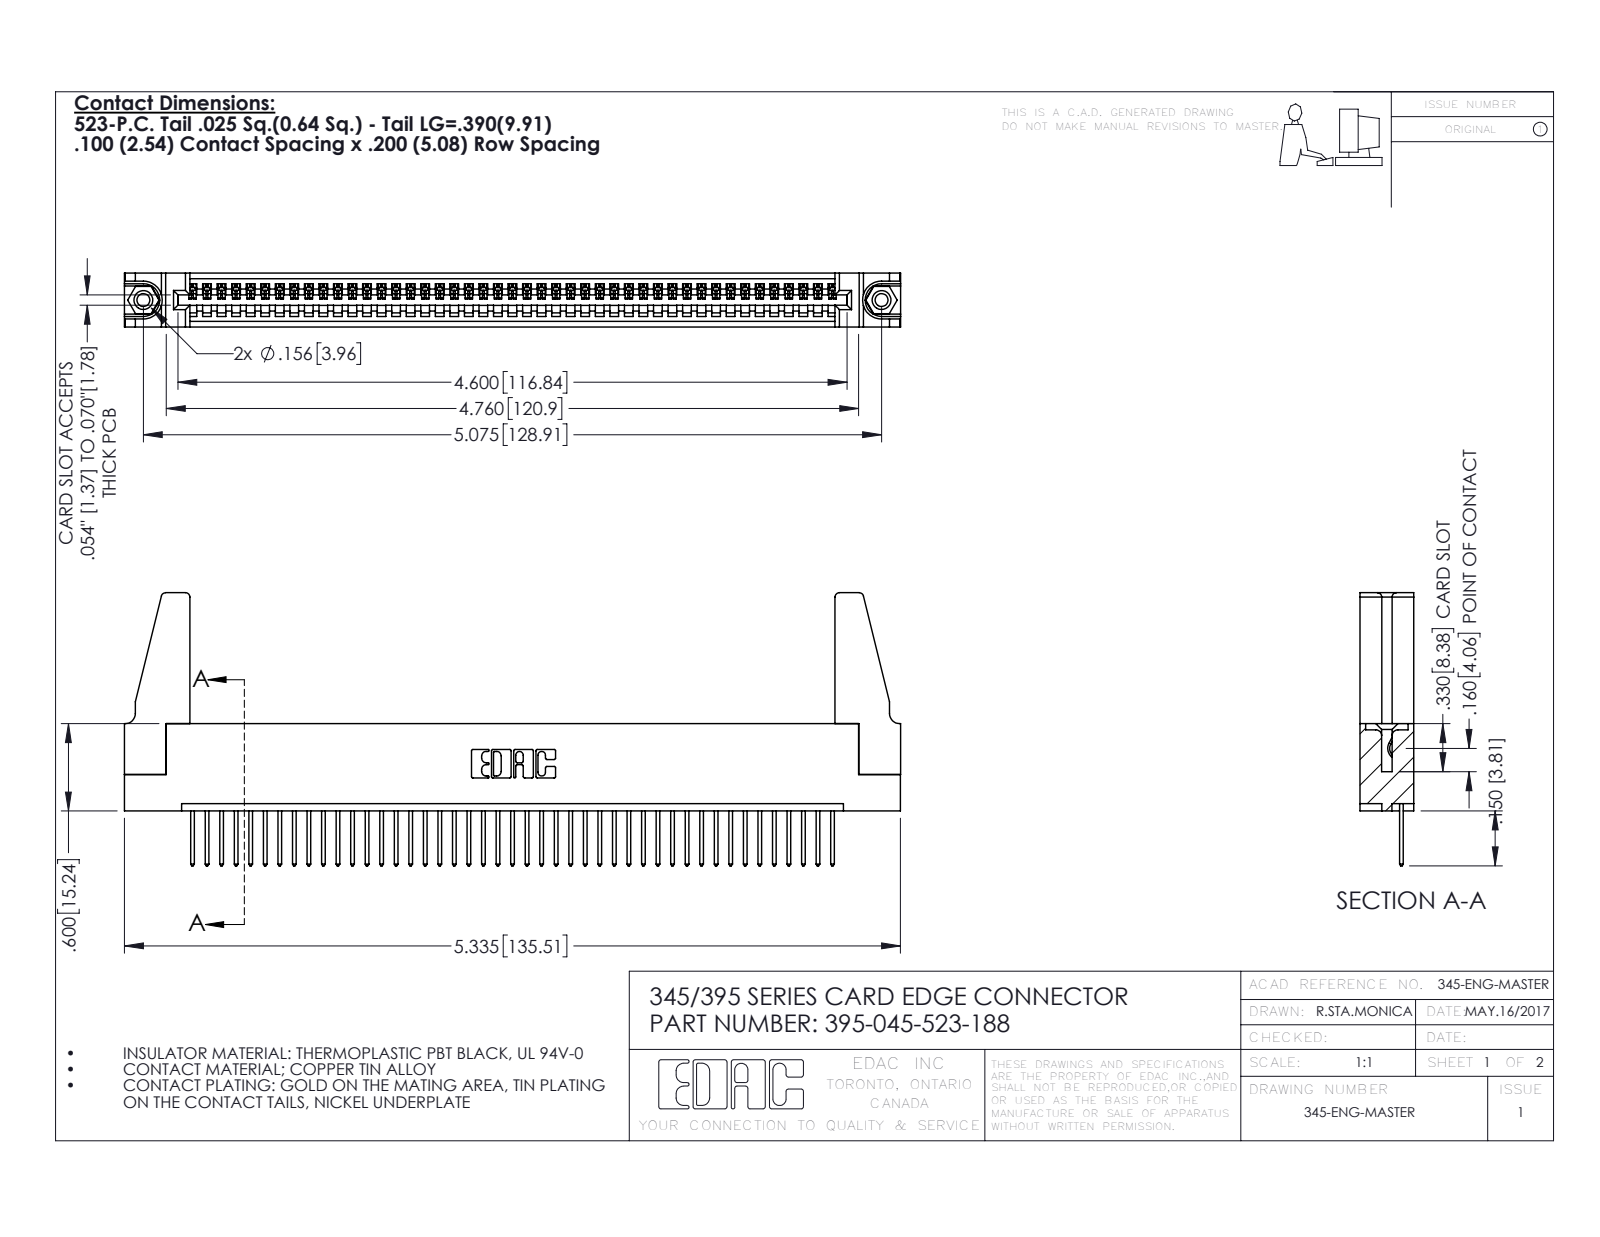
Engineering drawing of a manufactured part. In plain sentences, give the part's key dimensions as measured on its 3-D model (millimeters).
The part is named "345-220-078_345-220-088; 345-250-001_345-250-001-102; 345-292-001_345-293-123; 395-045-523-188 (+1 more)". Its 3-D file was written by "SolidWorks 2016 (CONFIG_CONTROL_DESIGN)". It is 50 solids with 2860 faces: 1952 planar, 892 cylindrical and 16 other. Overall it measures 135.5 by 47.7 by 9.4 millimeters. Its volume is 16 100 cubic millimeters and its surface area 20 340 square millimeters. Round holes: 2 of diameter 2.3, 2 of diameter 3.2, 2 of diameter 4, 1 of diameter 1.6. Round bosses or shafts: 2 of diameter 3.9. Partial cylindrical surfaces (rounded edges, fillets, slot ends): 90 of radius 0.2, 90 of radius 0.3, 22 of radius 0.3, 8 of radius 0.8, 6 of radius 0.2, 6 of radius 0.8, 3 of radius 0.7, 2 of radius 0.8. The main face-to-face distances are 1.8, 7.6, 9.4, 5.1, 2.5, 6.9, 0.6, 5.7, 3.8, 1.8. The hole center spacings are 6.9, 122.9, 128.9.
